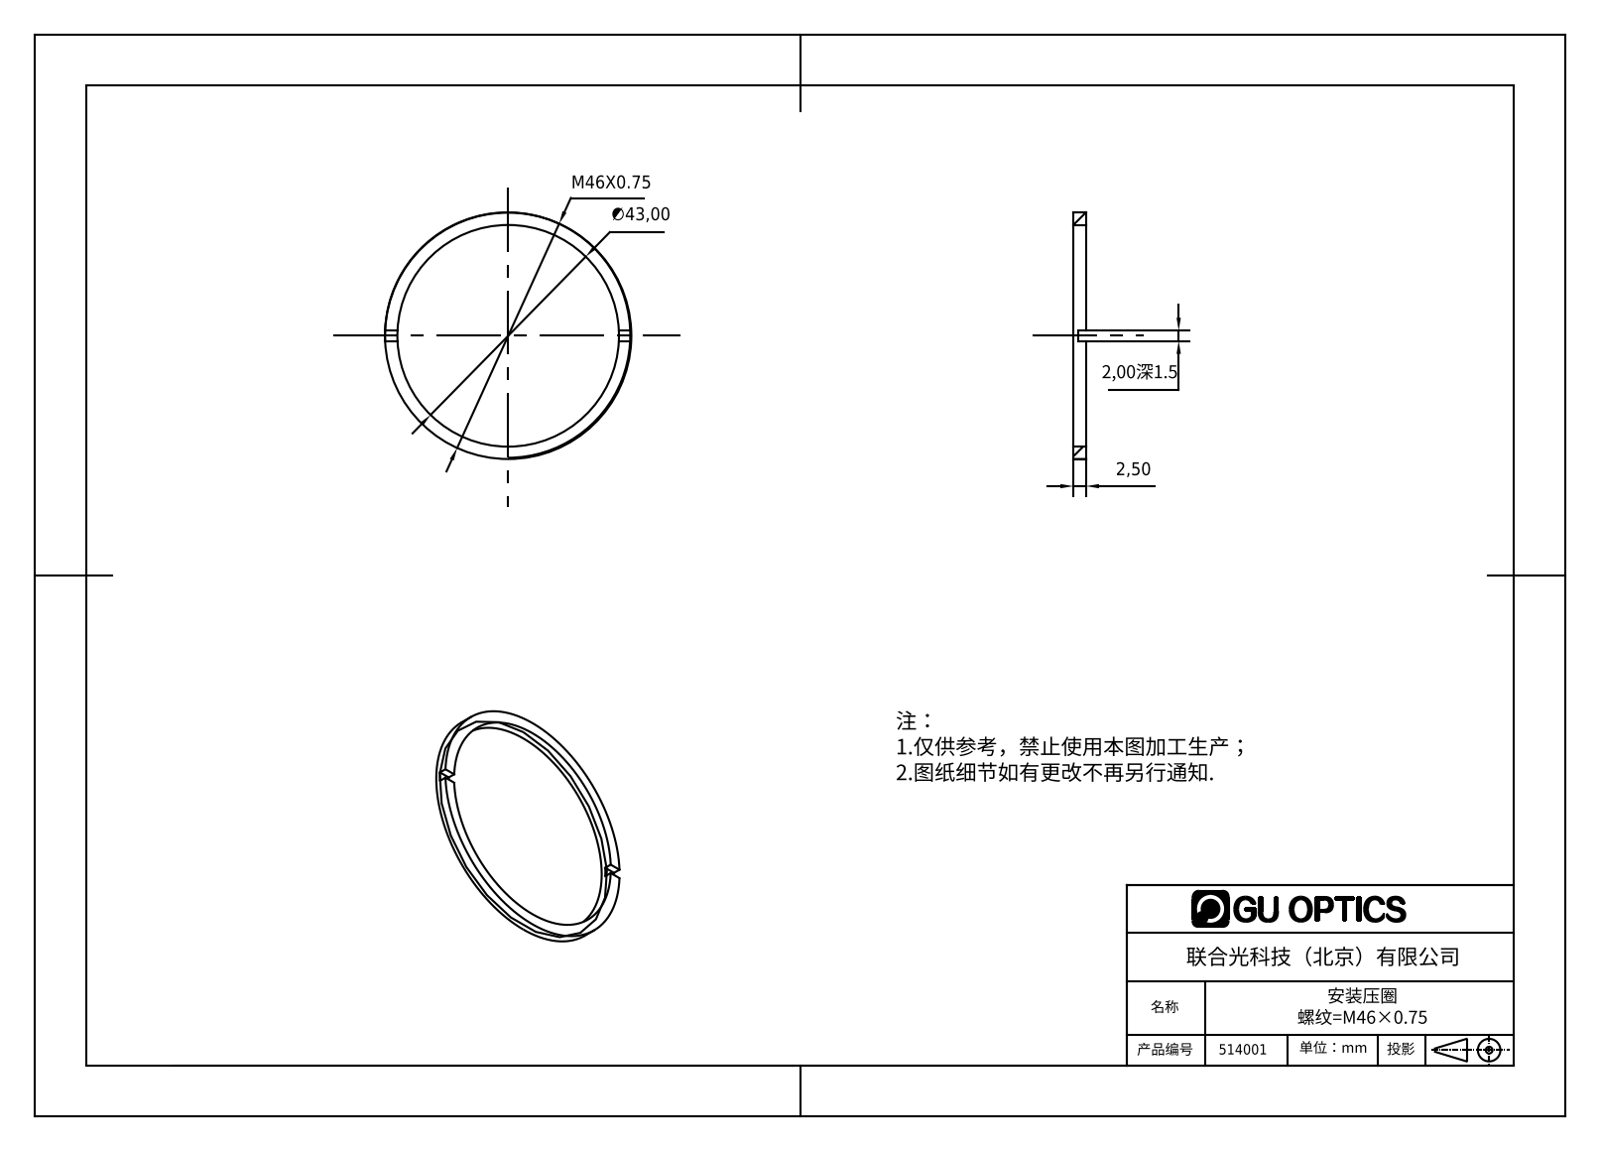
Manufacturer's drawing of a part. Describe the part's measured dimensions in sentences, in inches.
The part is named "514002". Its 3-D file was written by "SolidWorks 2016 (AUTOMOTIVE_DESIGN)". It is 1 solid with 13 faces: 9 planar, 4 cylindrical and 0 other. Overall it measures 1.803 by 1.803 by 0.098 inches. Its volume is 0.029 cubic inches and its surface area 1.68 square inches. Round holes: 1 of diameter 1.693. Round bosses or shafts: 1 of diameter 1.803. The main face-to-face distances are 0.098, 0.039, 0.059, 0.079.
